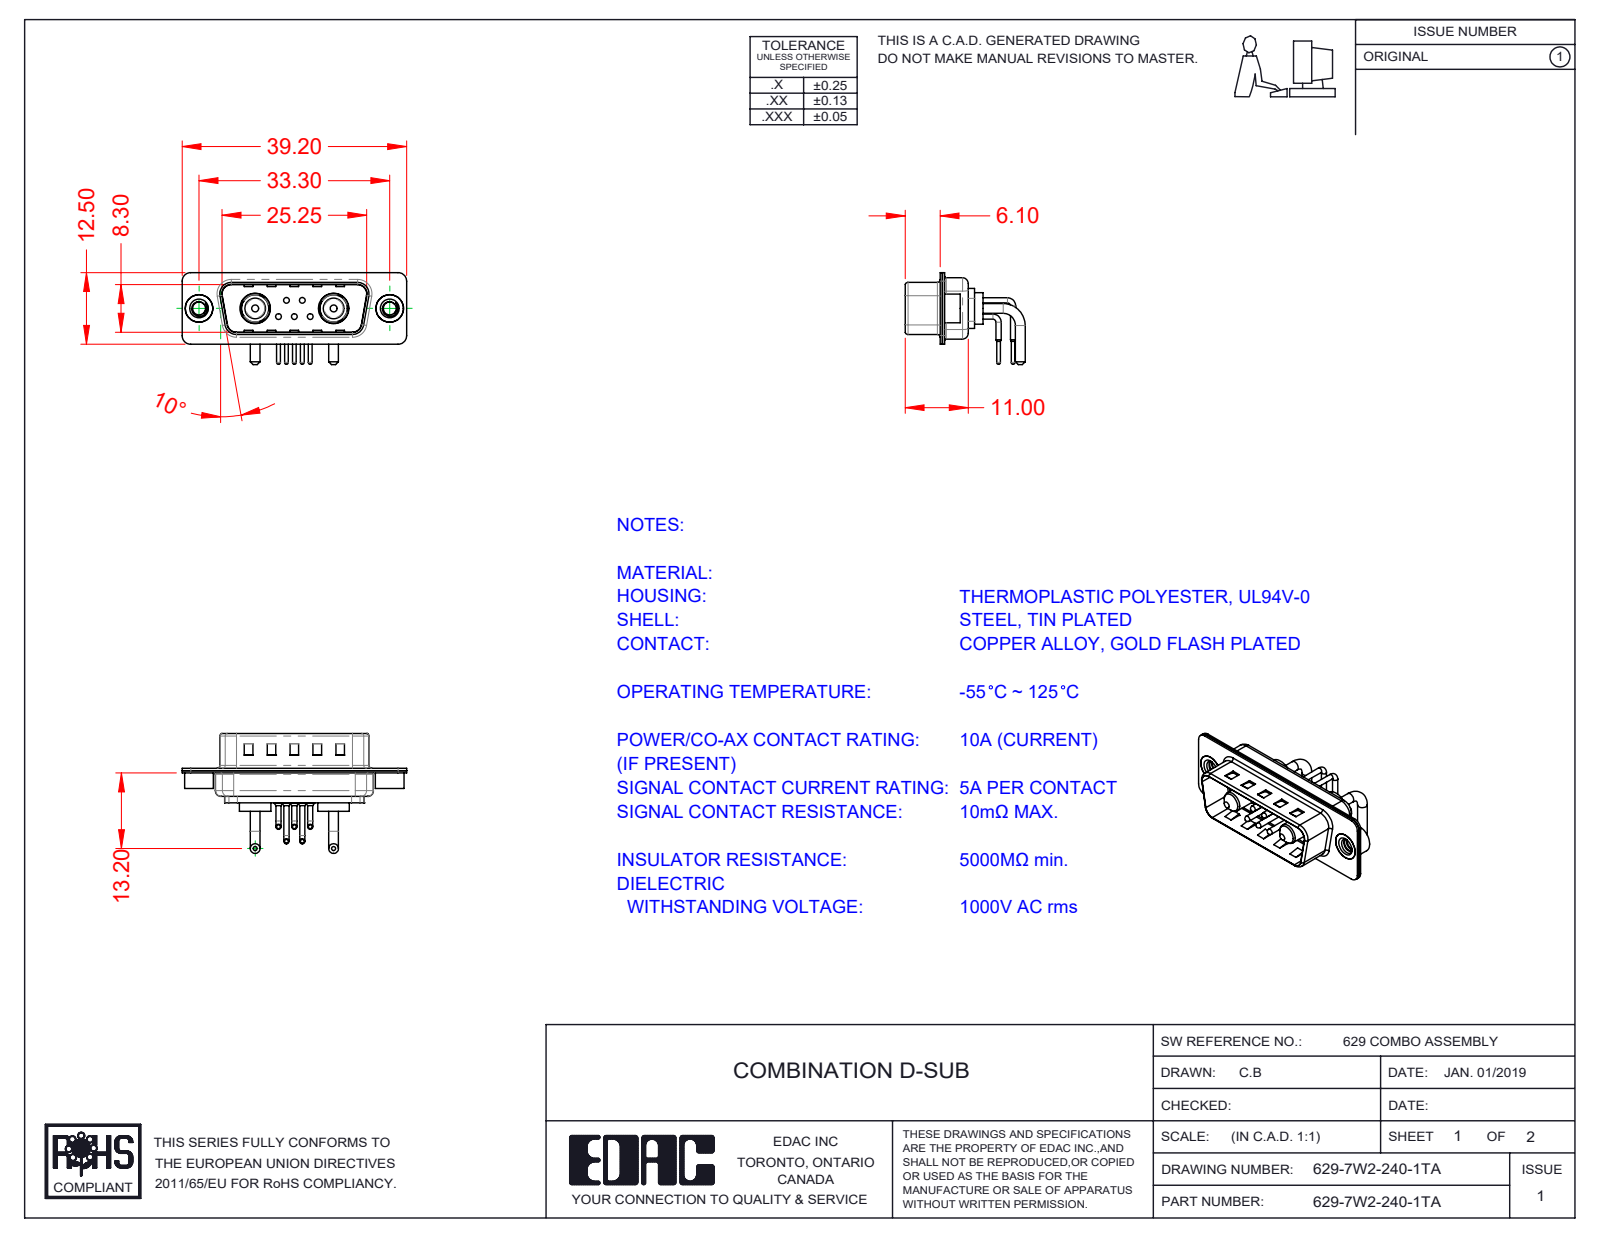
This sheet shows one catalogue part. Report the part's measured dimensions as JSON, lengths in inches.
{"part_name": "Power Pin_10A RA; 629Combo Threaded Rivet_2; 629-7W2-240-1TA; 629Combo Contact Row 1 (+4 more)", "step_written_by": "SolidWorks 2020 (CONFIG_CONTROL_DESIGN)", "units": "inches", "bodies": {"solids": 14, "faces": 976, "planar": 479, "cylindrical": 355, "other": 142}, "overall_size": [1.543, 0.825, 0.632], "volume_in3": 0.124, "surface_area_in2": 7.738, "round_holes": [[0.03, 5], [0.063, 5], [0.079, 5], [0.089, 2], [0.157, 2], [0.189, 2], [0.191, 2], [0.209, 2]], "round_bosses_or_shafts": [[0.035, 10], [0.059, 5], [0.039, 5], [0.026, 5], [0.067, 4], [0.217, 2], [0.205, 2], [0.197, 2]], "partial_cylinders_radius": [[0.059, 16], [0.079, 12], [0.02, 8], [0.063, 8], [0.04, 5], [0.01, 4], [0.024, 4], [0.026, 4]], "face_to_face_distances": [0.016, 0.031, 0.374, 0.358, 0.343, 0.39, 0.03, 0.047, 0.22, 0.014], "hole_center_spacings": [0.124, 0.109, 0.386, 0.925, 0.17, 0.17, 0.198, 0.198]}
